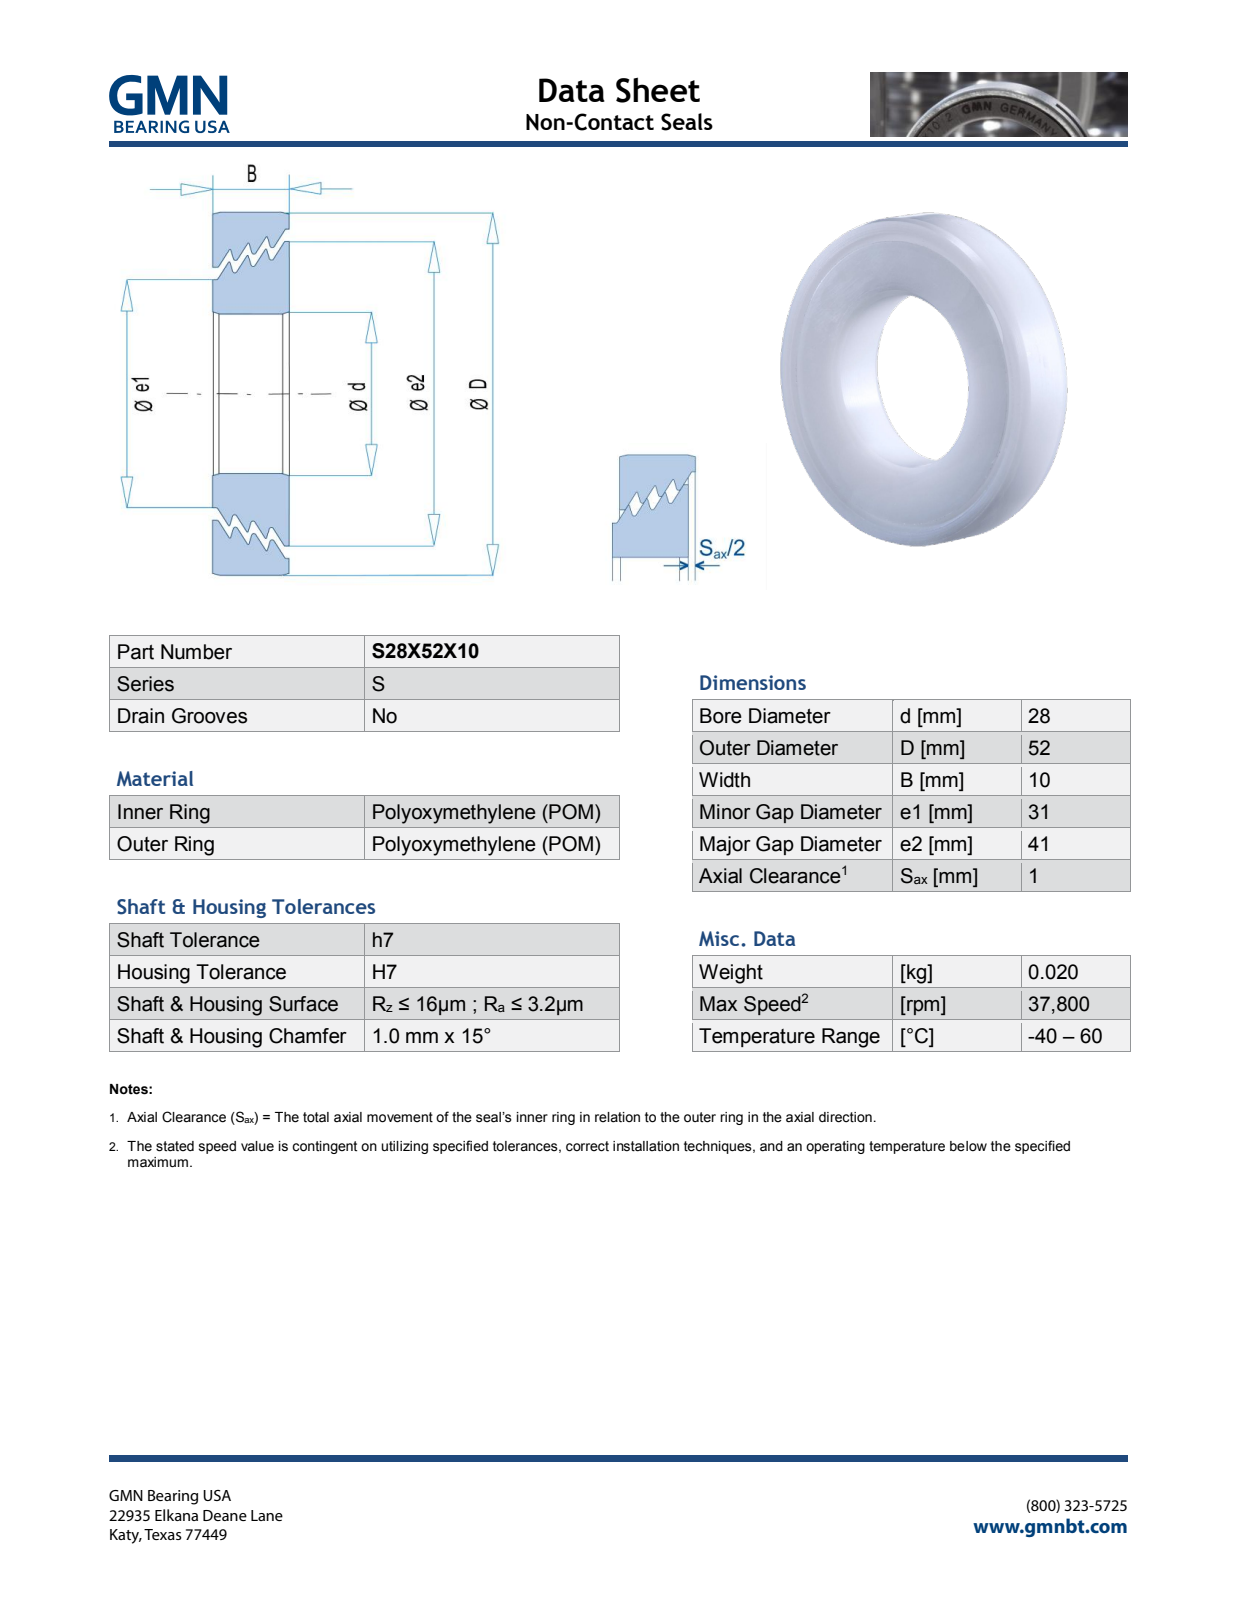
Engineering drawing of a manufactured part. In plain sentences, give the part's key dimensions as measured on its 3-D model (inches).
The part is named "S28X52X10_PRT". Its 3-D file was written by "PRO/ENGINEER BY PARAMETRIC TECHNOLOGY CORPORATION, 2013150 (AUTOMOTIVE_DESIGN)". It is 2 solids with 661 faces: 581 planar, 12 cylindrical and 68 other. Overall it measures 2.047 by 2.047 by 0.396 inches. Its volume is 0.859 cubic inches and its surface area 15.51 square inches. Round holes: 1 of diameter 1.102, 1 of diameter 1.285, 1 of diameter 1.678. Round bosses or shafts: 1 of diameter 2.047, 1 of diameter 1.614, 1 of diameter 1.22. The main face-to-face distances are 0.394, 0.396, 0.066, 0.058, 0.05, 0.067, 0.047, 0.03, 0.058, 0.056.
